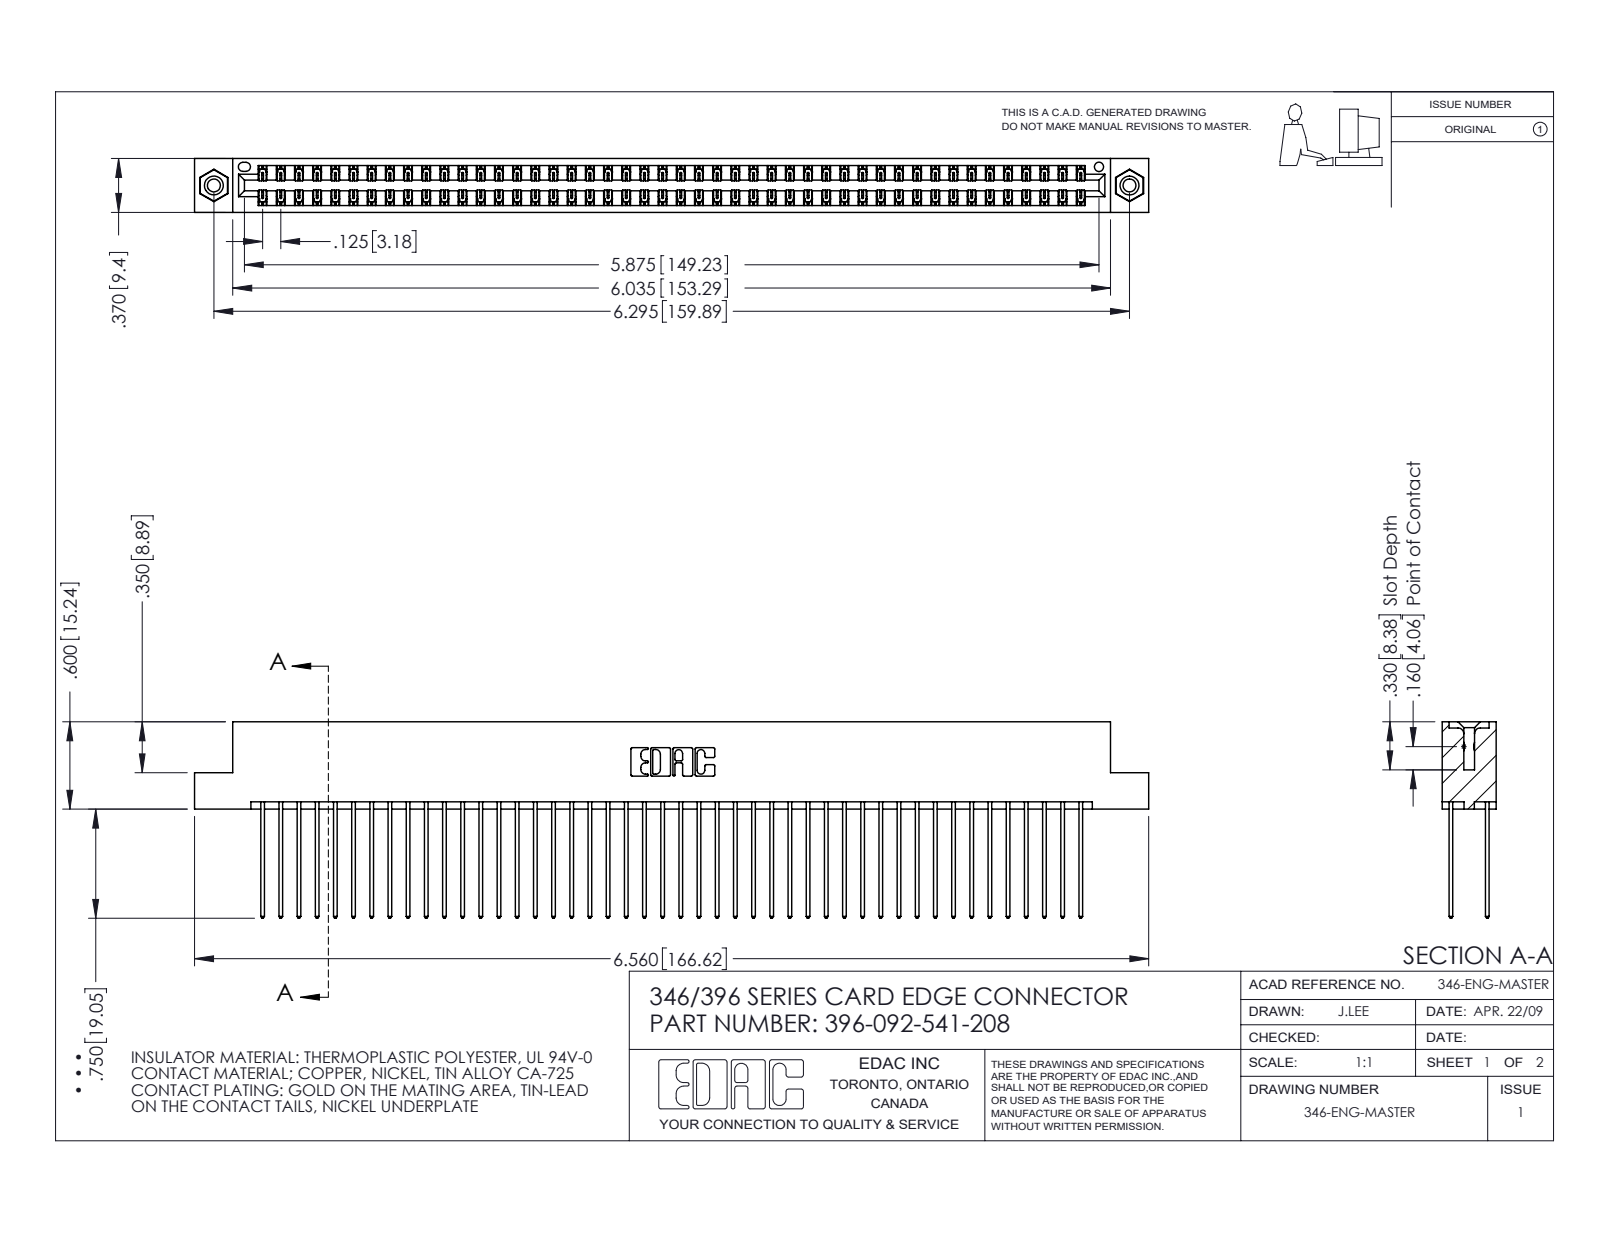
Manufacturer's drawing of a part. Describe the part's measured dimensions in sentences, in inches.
The part is named "346 Part_Flush Mounting Lugs - 0.156 Dia-TI; 345-292-001_345-293-141; 396-092-541-208; 345-250-001_345-250-003-102". Its 3-D file was written by "SolidWorks 2016 (CONFIG_CONTROL_DESIGN)". It is 95 solids with 4966 faces: 3328 planar, 1622 cylindrical and 16 other. Overall it measures 6.56 by 1.35 by 0.37 inches. Its volume is 1.025 cubic inches and its surface area 39.85 square inches. Round holes: 2 of diameter 0.089, 2 of diameter 0.125, 2 of diameter 0.156, 1 of diameter 0.064. Round bosses or shafts: 2 of diameter 0.155. Partial cylindrical surfaces (rounded edges, fillets, slot ends): 138 of radius 0.006, 92 of radius 0.01, 22 of radius 0.01, 6 of radius 0.007, 6 of radius 0.031, 3 of radius 0.026, 2 of radius 0.014, 2 of radius 0.022. The main face-to-face distances are 0.048, 0.322, 0.25, 0.072, 0.298, 0.025, 0.37, 0.275, 0.225, 0.148. The hole center spacings are 0.246, 6.086, 6.295.
